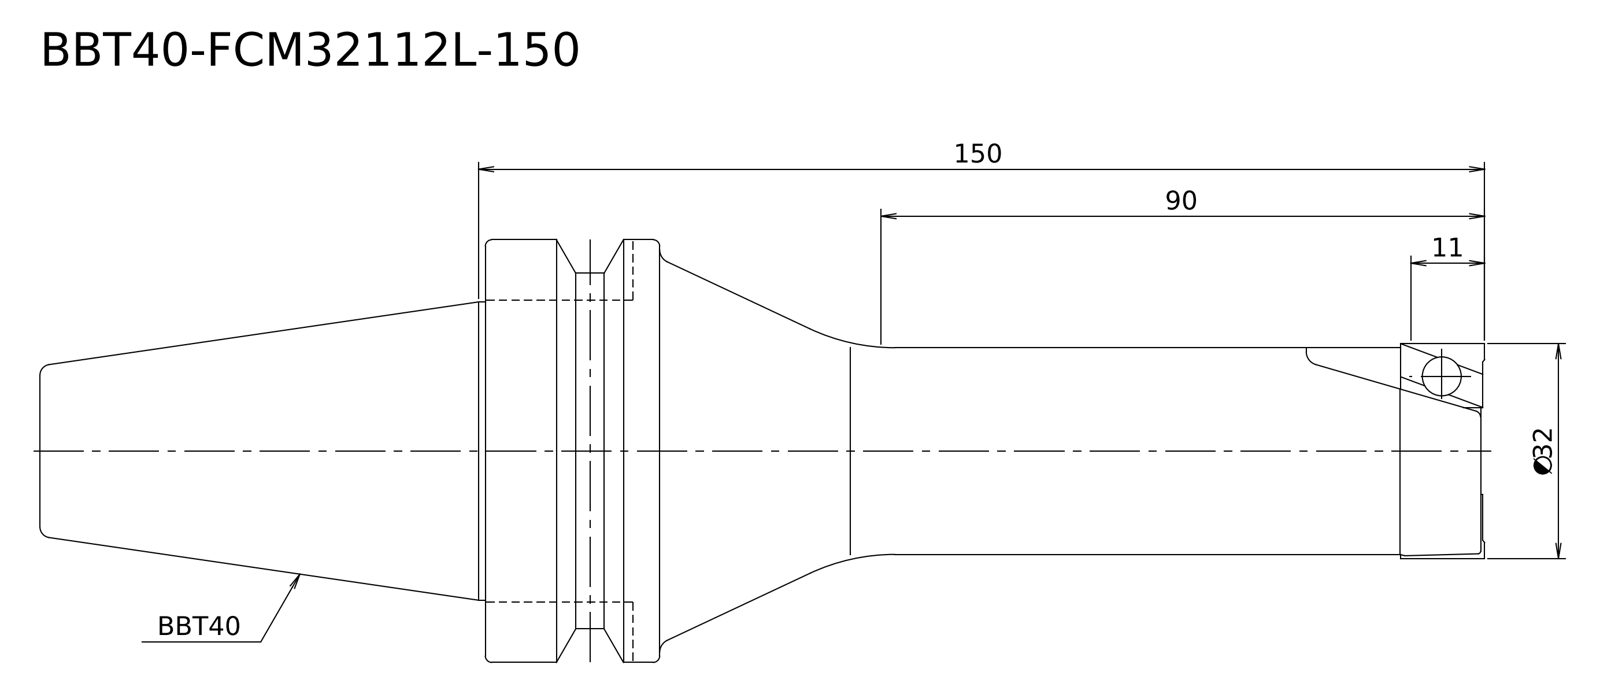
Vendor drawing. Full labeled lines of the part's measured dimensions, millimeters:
STEP written by: Kubotek KeyCreator V8.5.1 (14335) (CONFIG_CONTROL_DESIGN)
Units: millimetres
Bodies: 1 solid, 17 faces (4 planar, 6 cylindrical, 7 other)
Overall size (bounding box): 215.4 × 63 × 63
Volume: 257 260 mm³ · Surface area: 30 277 mm²
Round bosses / shafts (diameter × count): ⌀63 ×1, ⌀53 ×1, ⌀44.45 ×1, ⌀32 ×1, ⌀30.8 ×1
Main face-to-face distances: 149, 215.4, 66.4, 123, 26, 92.4
